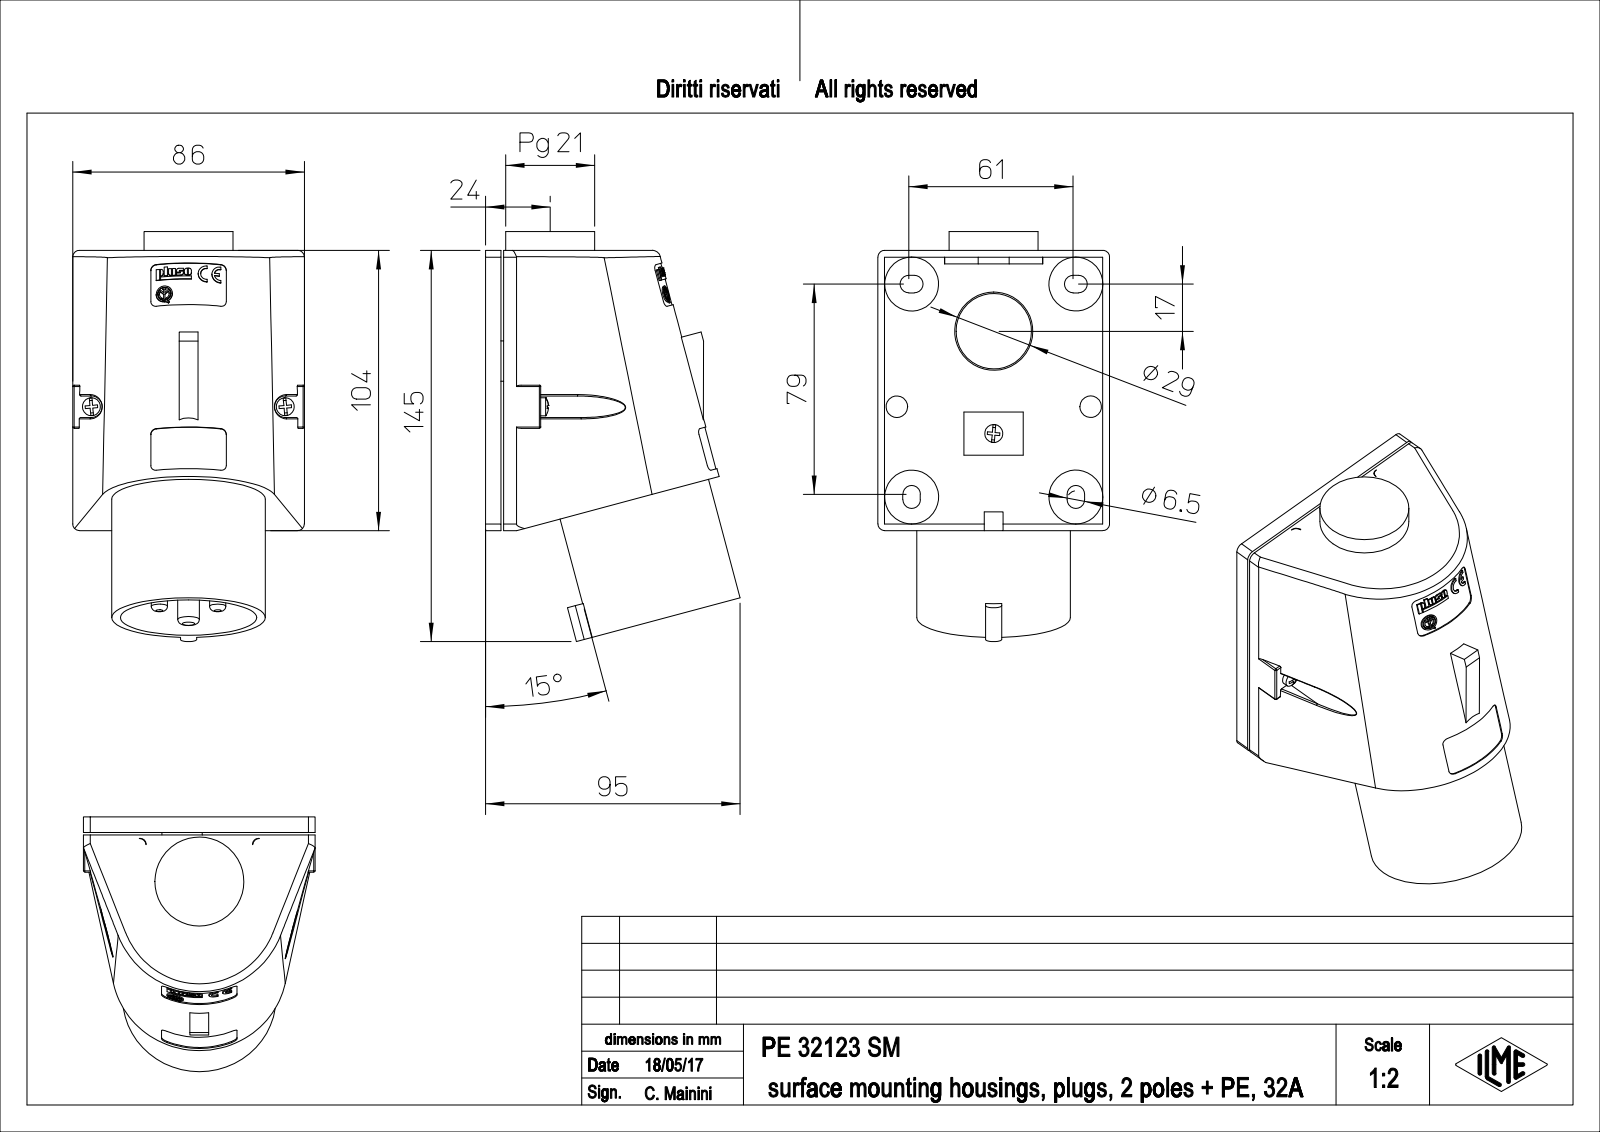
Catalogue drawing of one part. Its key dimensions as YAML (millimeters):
part_name: "PE_32123_SM"
step_written_by: "PTC Creo Elements/Direct Modeling 19.0E 27-Jun-2016 (C) Parametric Technology GmbH (AUTOMOTIVE_DESIGN)"
units: millimeters
bodies: {solids: 1, faces: 1004, planar: 657, cylindrical: 213, other: 134}
overall_size: [152.14, 94.53, 86]
volume: 491313
surface_area: 90882
round_holes:
  - {diameter: 2.8, count: 2}
  - {diameter: 3.2, count: 2}
  - {diameter: 4, count: 2}
  - {diameter: 4.5, count: 2}
  - {diameter: 6.1, count: 2}
  - {diameter: 4.2, count: 1}
  - {diameter: 5.04, count: 1}
  - {diameter: 27.54, count: 1}
  - {diameter: 29, count: 1}
  - {diameter: 32, count: 1}
  - {diameter: 50.6, count: 1}
round_bosses_or_shafts:
  - {diameter: 6.7, count: 5}
  - {diameter: 20, count: 4}
  - {diameter: 8, count: 3}
  - {diameter: 6, count: 3}
  - {diameter: 3, count: 2}
  - {diameter: 57, count: 1}
  - {diameter: 50, count: 1}
  - {diameter: 33, count: 1}
partial_cylinders:
  - {radius: 0.5, count: 22}
  - {radius: 0.17, count: 11}
  - {radius: 2, count: 10}
  - {radius: 0.86, count: 9}
  - {radius: 3.25, count: 8}
  - {radius: 2.5, count: 6}
  - {radius: 0.3, count: 4}
  - {radius: 4.5, count: 4}
face_to_face_distances: [0.98, 4.75, 5.73, 1, 7, 5.75, 6.73, 2.25, 2.5, 8]
hole_center_spacings: [12.51, 21, 37.36, 45.61, 72, 11.94, 21.66, 23.48]
